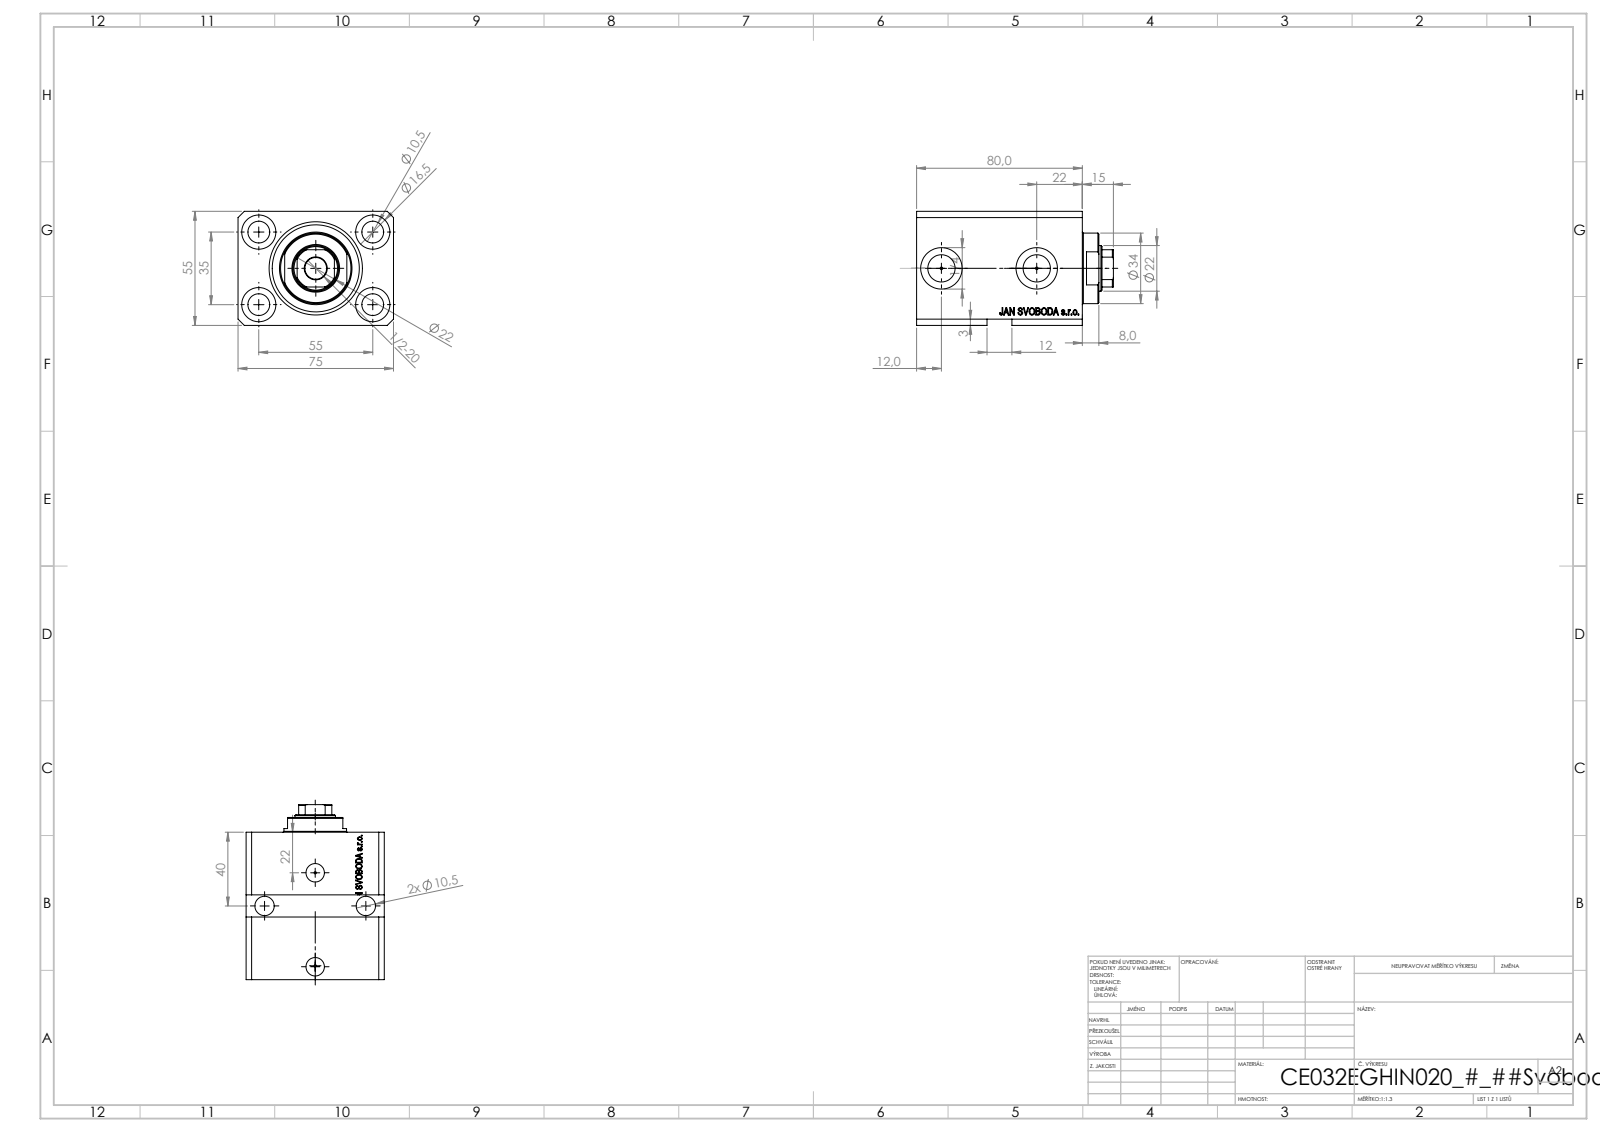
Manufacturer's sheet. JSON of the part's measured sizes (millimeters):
{"part_name": "V250CE_C_VCP; V250CE_VC_E; V250CE_E_Body", "step_written_by": "SolidWorks 2019 (CONFIG_CONTROL_DESIGN)", "units": "millimeters", "bodies": {"solids": 3, "faces": 894, "planar": 438, "cylindrical": 84, "other": 372}, "overall_size": [95, 75, 55], "volume_mm3": 275455, "surface_area_mm2": 67234, "round_holes": [[10.5, 7], [1.25, 4], [16.5, 4], [10, 2], [13.16, 2], [20, 2], [22, 1], [32, 1], [45, 1]], "round_bosses_or_shafts": [[34, 1]], "partial_cylinders_radius": [[10.5, 1]], "face_to_face_distances": [55, 75, 15, 80, 65, 9.9, 55.1, 70.1, 11, 69], "hole_center_spacings": [32.6, 55, 32.87, 35, 42.55, 42.96, 65.19, 0.53]}
